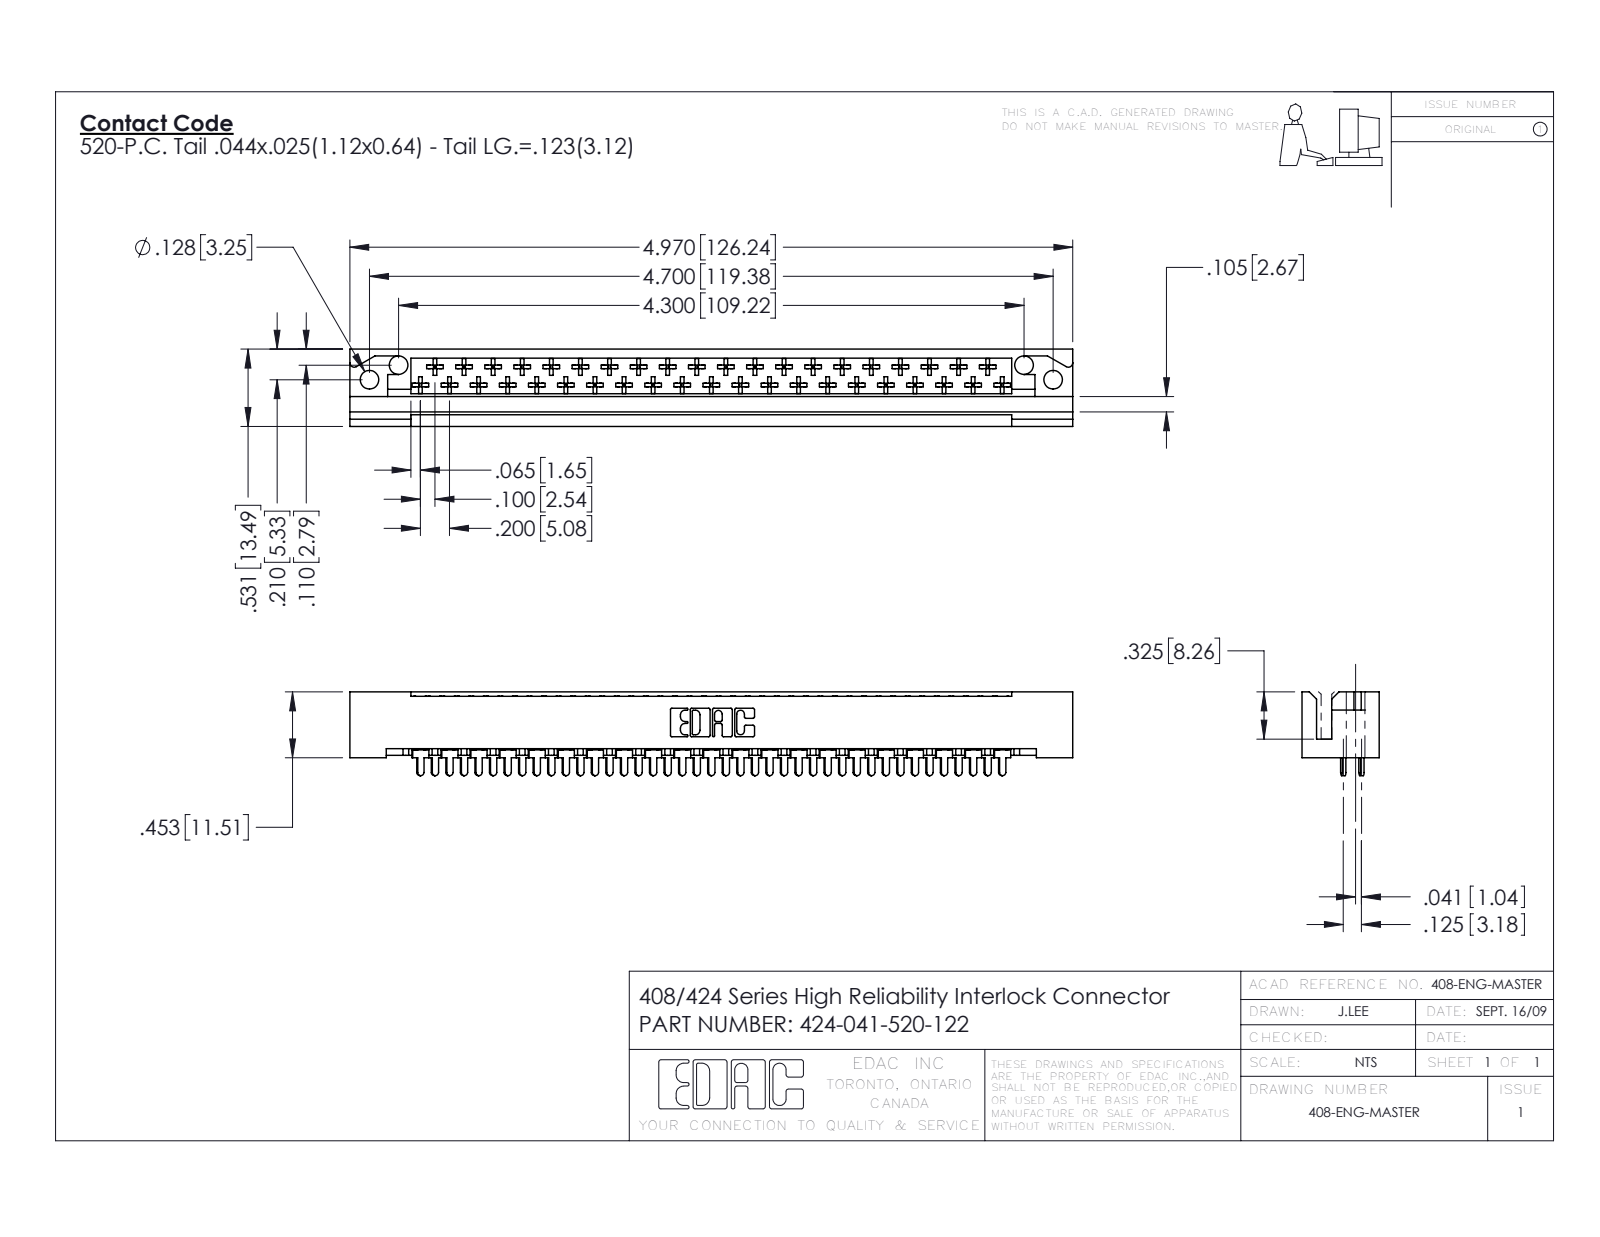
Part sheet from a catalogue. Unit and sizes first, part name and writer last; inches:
Units: inches
Overall size (bounding box): 4.97 × 0.576 × 0.531
Round holes (diameter × count): ⌀0.128 ×4
Partial cylindrical surfaces — rounded edges, fillets, slot ends (radius × count): R0.01 ×246, R0.02 ×43, R0.022 ×41, R0.01 ×22, R0.007 ×6, R0.031 ×6, R0.026 ×3, R0.03 ×2
Main face-to-face distances: 0.1, 0.296, 0.025, 0.531, 0.125, 0.272, 0.235, 0.259, 0.025, 0.217
Hole centre spacings: 0.224, 4.501, 4.3, 4.7
Volume: 0.796 in³ · Surface area: 26.48 in²
Bodies: 42 solids, 2400 faces (1811 planar, 425 cylindrical, 164 other)
Part name (STEP PRODUCT): 408-290-001_408-290-120; 424 Part_041; 424-041-520-122
STEP written by: SolidWorks 2016 (CONFIG_CONTROL_DESIGN)
